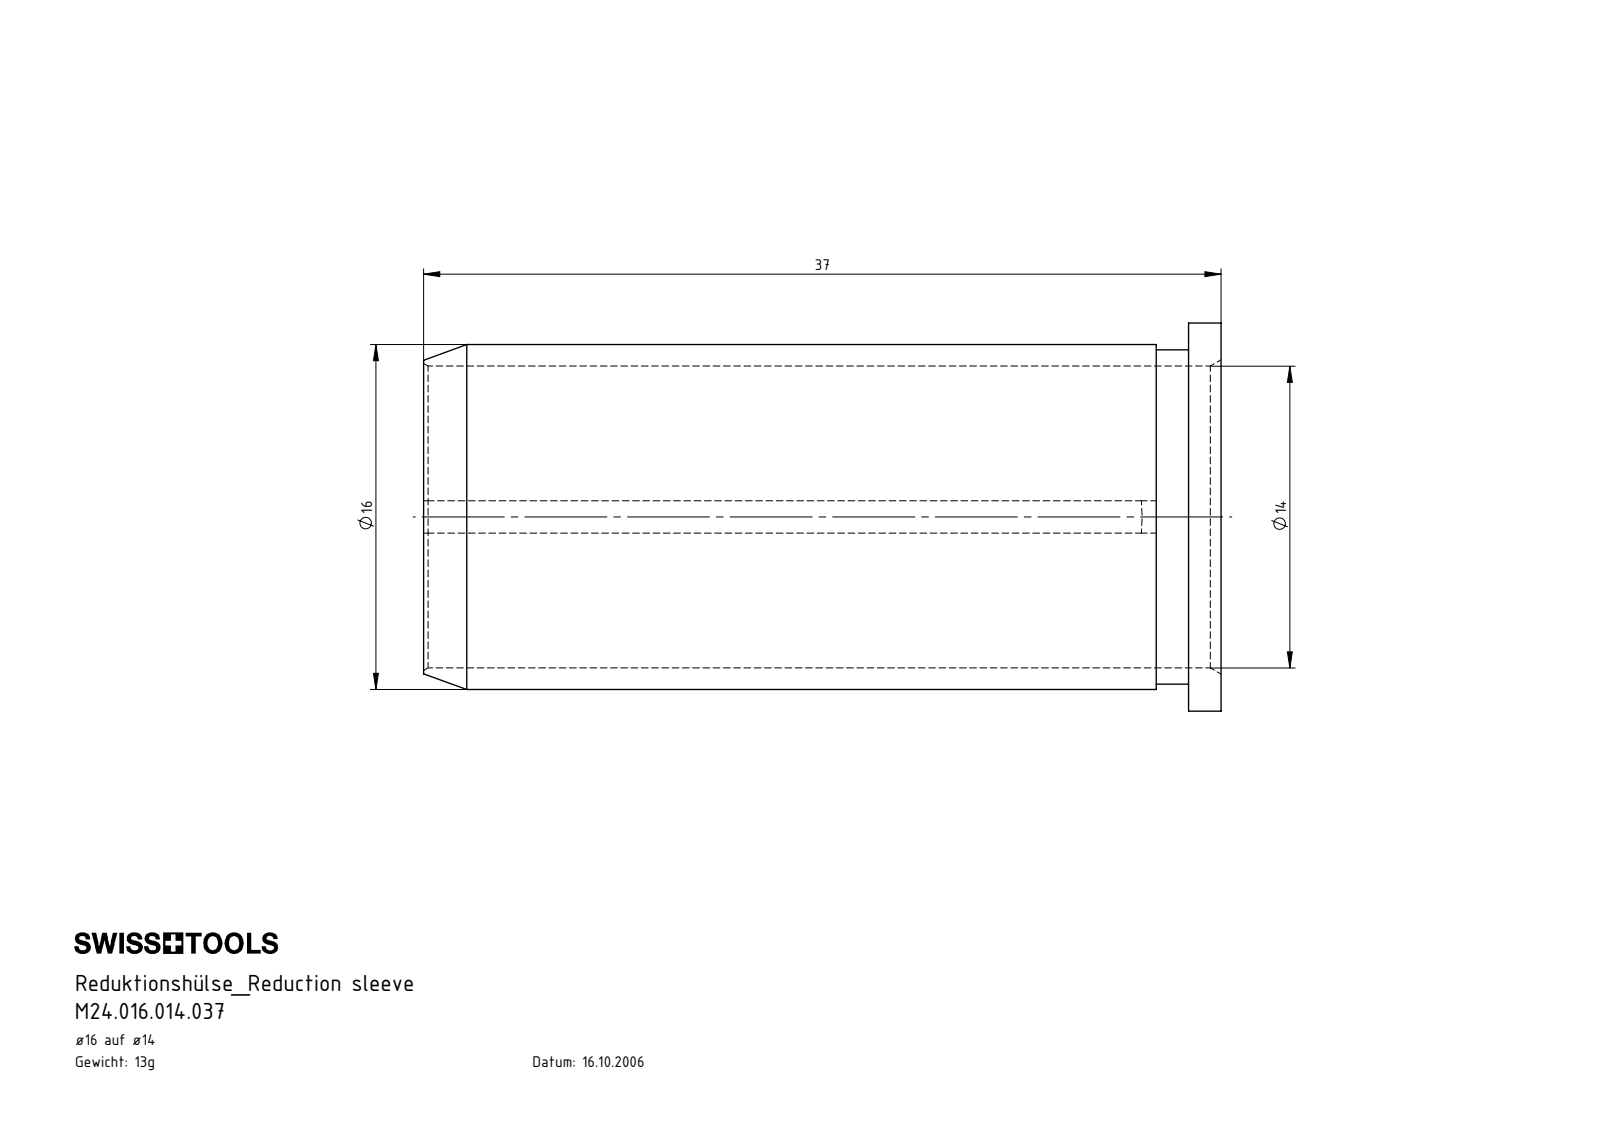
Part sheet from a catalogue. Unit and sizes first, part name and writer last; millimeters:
Units: millimetres
Overall size (bounding box): 37 × 18 × 18
Round holes (diameter × count): ⌀14 ×1
Round bosses / shafts (diameter × count): ⌀18 ×1, ⌀16 ×1, ⌀15.5 ×1
Partial cylindrical surfaces — rounded edges, fillets, slot ends (radius × count): R31.5 ×1
Main face-to-face distances: 1.5, 3, 34, 35.5, 37
Volume: 1 716 mm³ · Surface area: 3 640 mm²
Bodies: 1 solid, 14 faces (6 planar, 5 cylindrical, 3 other)
Part name (STEP PRODUCT): U14.U16.001.037
STEP written by: SolidWorks 2017 (AUTOMOTIVE_DESIGN)
